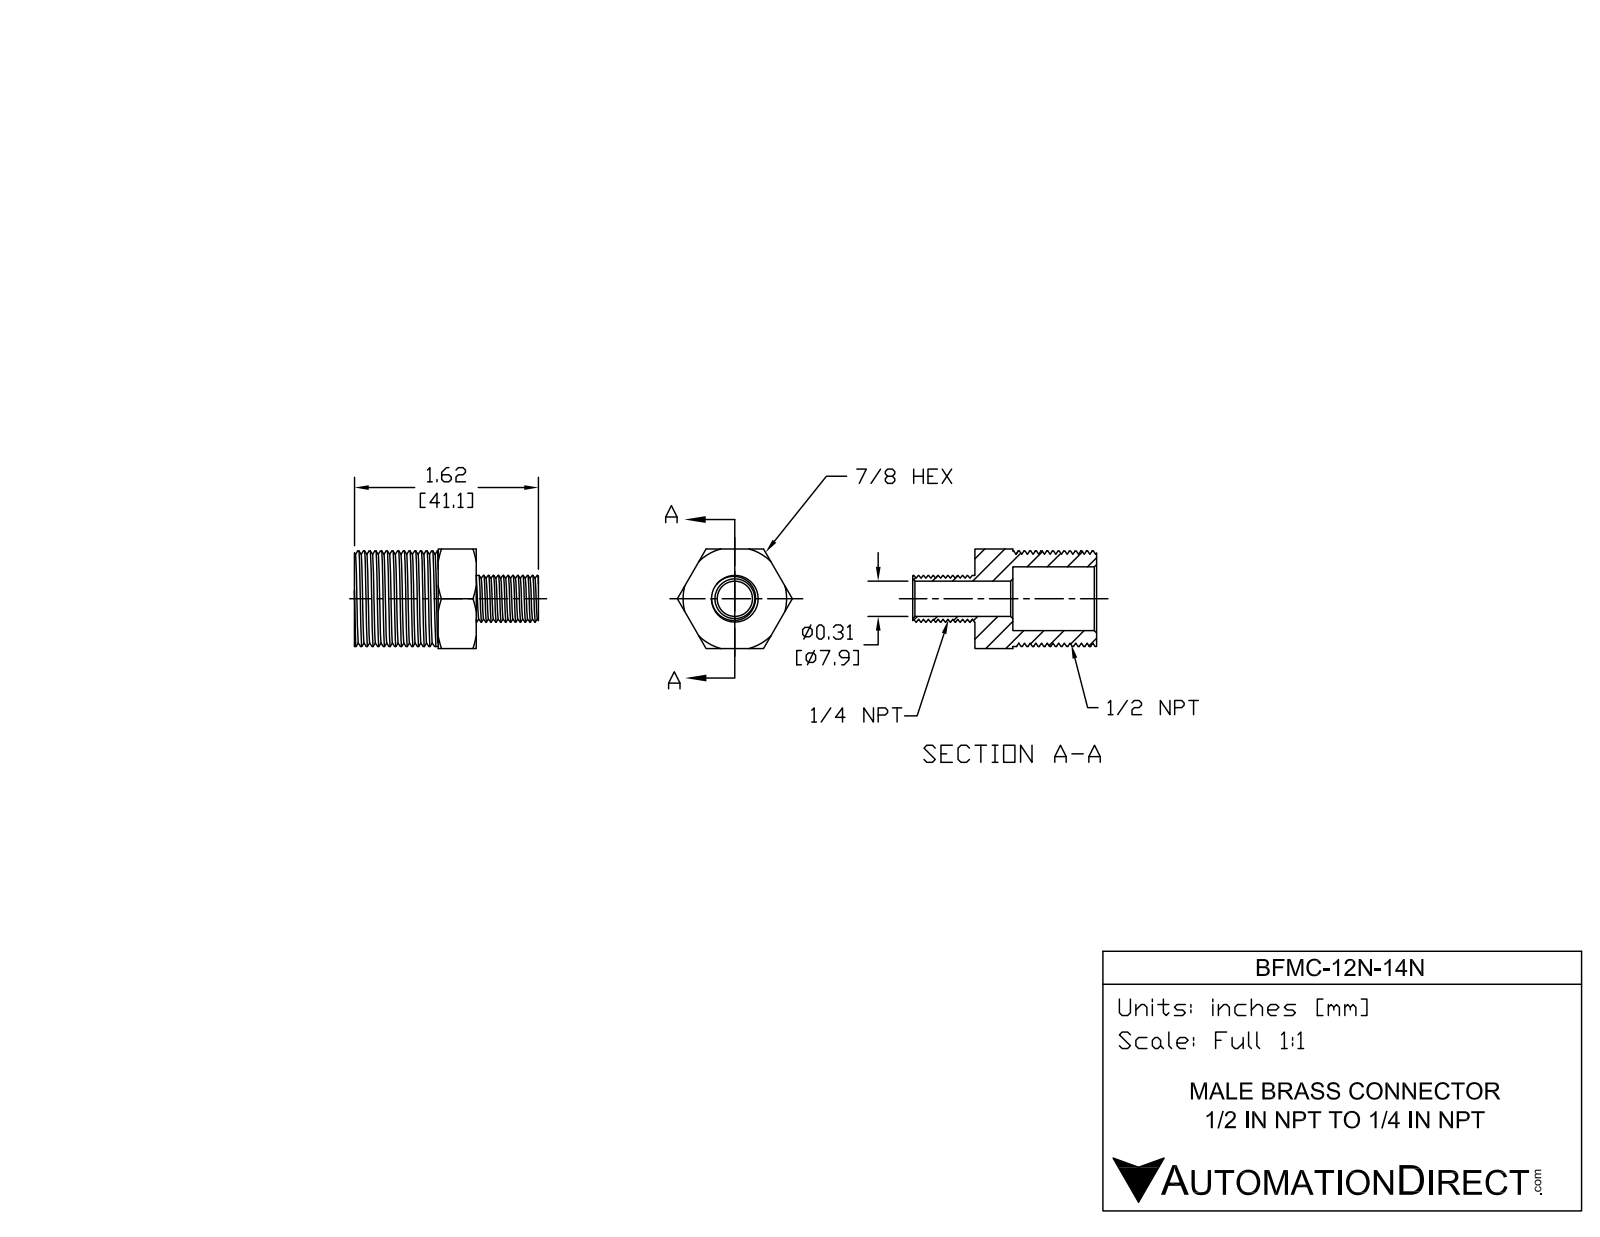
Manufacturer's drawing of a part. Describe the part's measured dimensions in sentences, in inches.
The part is named "BFMC-12N-14N". Its 3-D file was written by "SolidWorks 2015 (CONFIG_CONTROL_DESIGN)". It is 1 solid with 95 faces: 14 planar, 60 cylindrical and 21 other. Overall it measures 1.617 by 1.01 by 0.875 inches. Its volume is 0.424 cubic inches and its surface area 8.319 square inches. Round holes: 1 of diameter 0.31, 1 of diameter 0.56. Round bosses or shafts: 1 of diameter 0.84, 1 of diameter 0.41. The main face-to-face distances are 0.875, 1.07, 0.736, 0.334, 1.617, 0.881, 0.547, 0.437.
